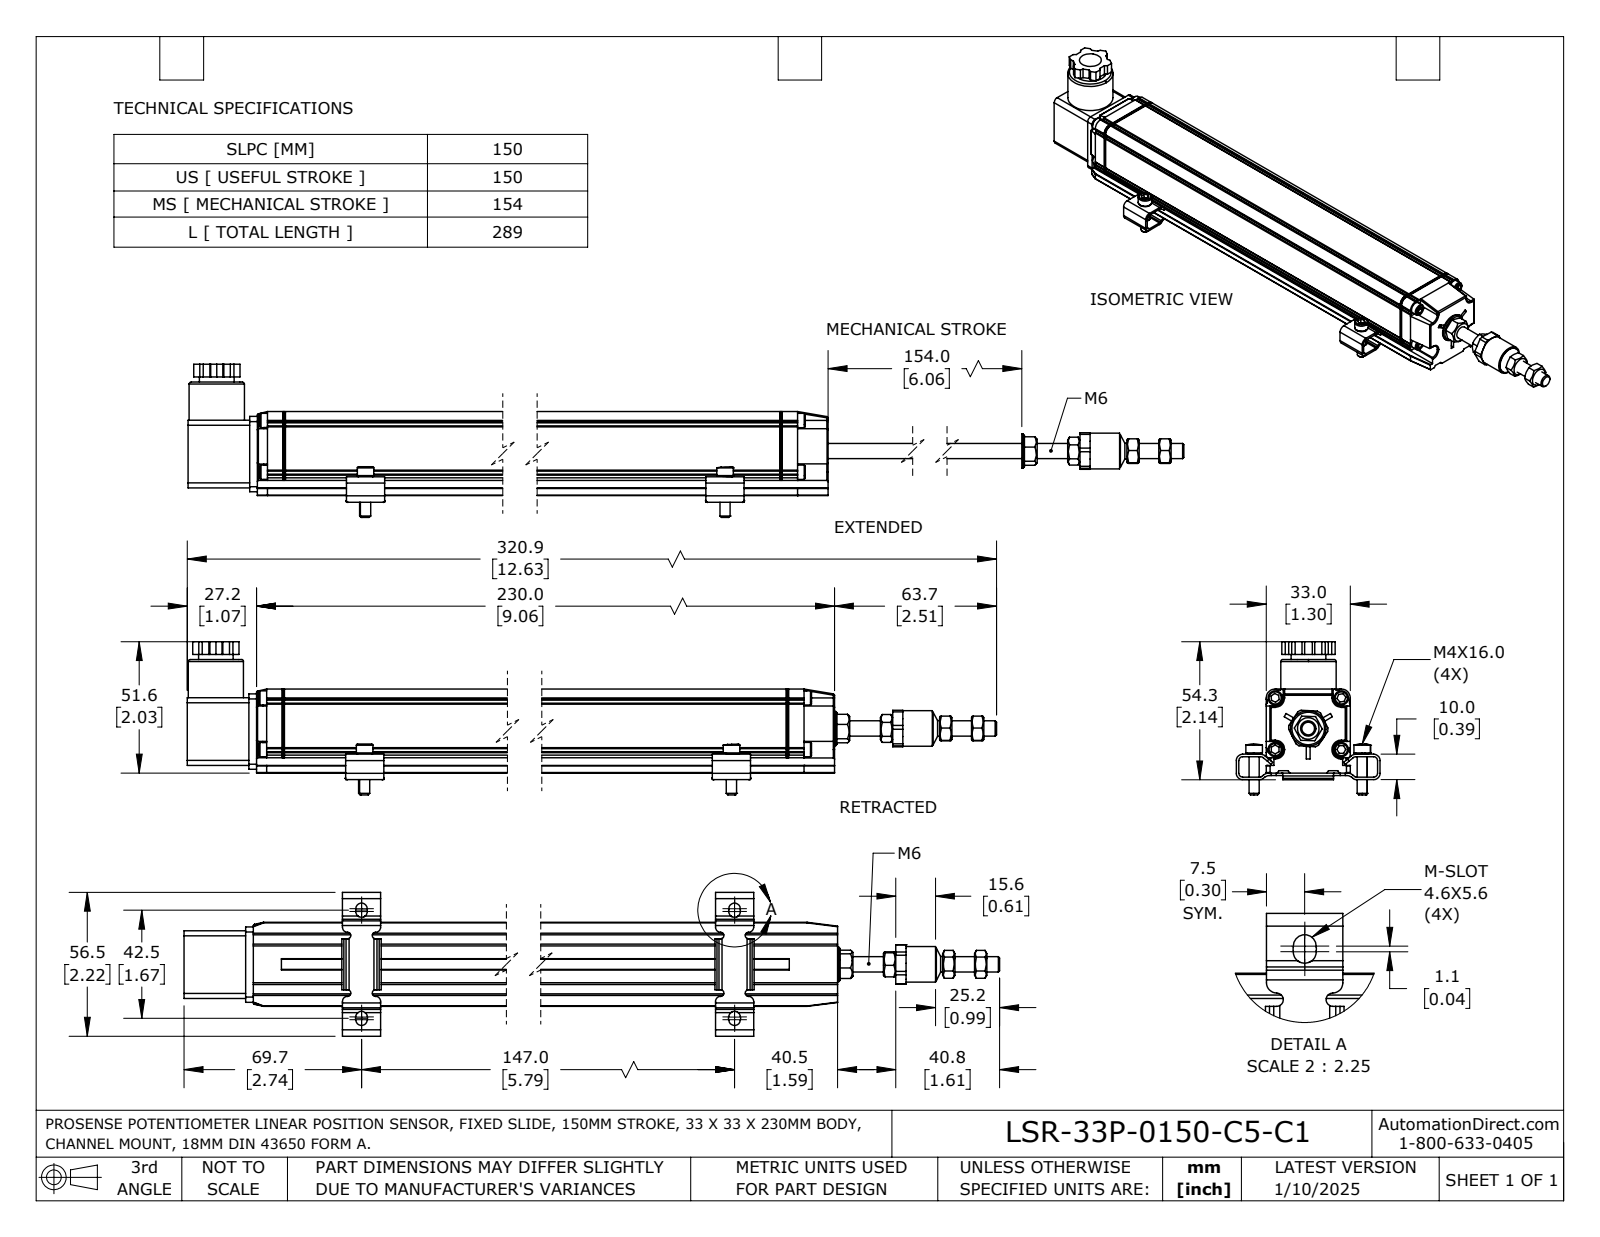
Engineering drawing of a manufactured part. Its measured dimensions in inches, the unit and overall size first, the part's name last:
Units: inches
Overall size (bounding box): 12.632 × 2.37 × 2.224
Round holes (diameter × count): ⌀0.106 ×4, ⌀0.13 ×4, ⌀0.11 ×1, ⌀0.169 ×1, ⌀0.205 ×1, ⌀0.209 ×1, ⌀0.232 ×1, ⌀0.276 ×1, ⌀0.285 ×1, ⌀0.354 ×1, ⌀0.394 ×1, ⌀0.413 ×1
Round bosses / shafts (diameter × count): ⌀0.157 ×5, ⌀0.118 ×5, ⌀0.256 ×4, ⌀0.22 ×4, ⌀0.854 ×1, ⌀0.551 ×1, ⌀0.535 ×1, ⌀0.528 ×1
Partial cylindrical surfaces — rounded edges, fillets, slot ends (radius × count): R0.079 ×28, R0.02 ×27, R0.008 ×16, R0.051 ×8, R0.059 ×8, R0.089 ×8, R0.118 ×8, R0.039 ×4
Main face-to-face distances: 1.299, 0.118, 0.039, 0.22, 1.181, 0.102, 0.063, 1.079, 0.079, 0.142
Hole centre spacings: 0.047, 0.583, 0.607, 0.696, 0.73, 0.799, 1.024, 1.299
Volume: 15.28 in³ · Surface area: 120.2 in²
Bodies: 15 solids, 1089 faces (728 planar, 275 cylindrical, 86 other)
Part name (STEP PRODUCT): LSR-33P-0150-C5-C1
STEP written by: SolidWorks 2023 (AUTOMOTIVE_DESIGN)
